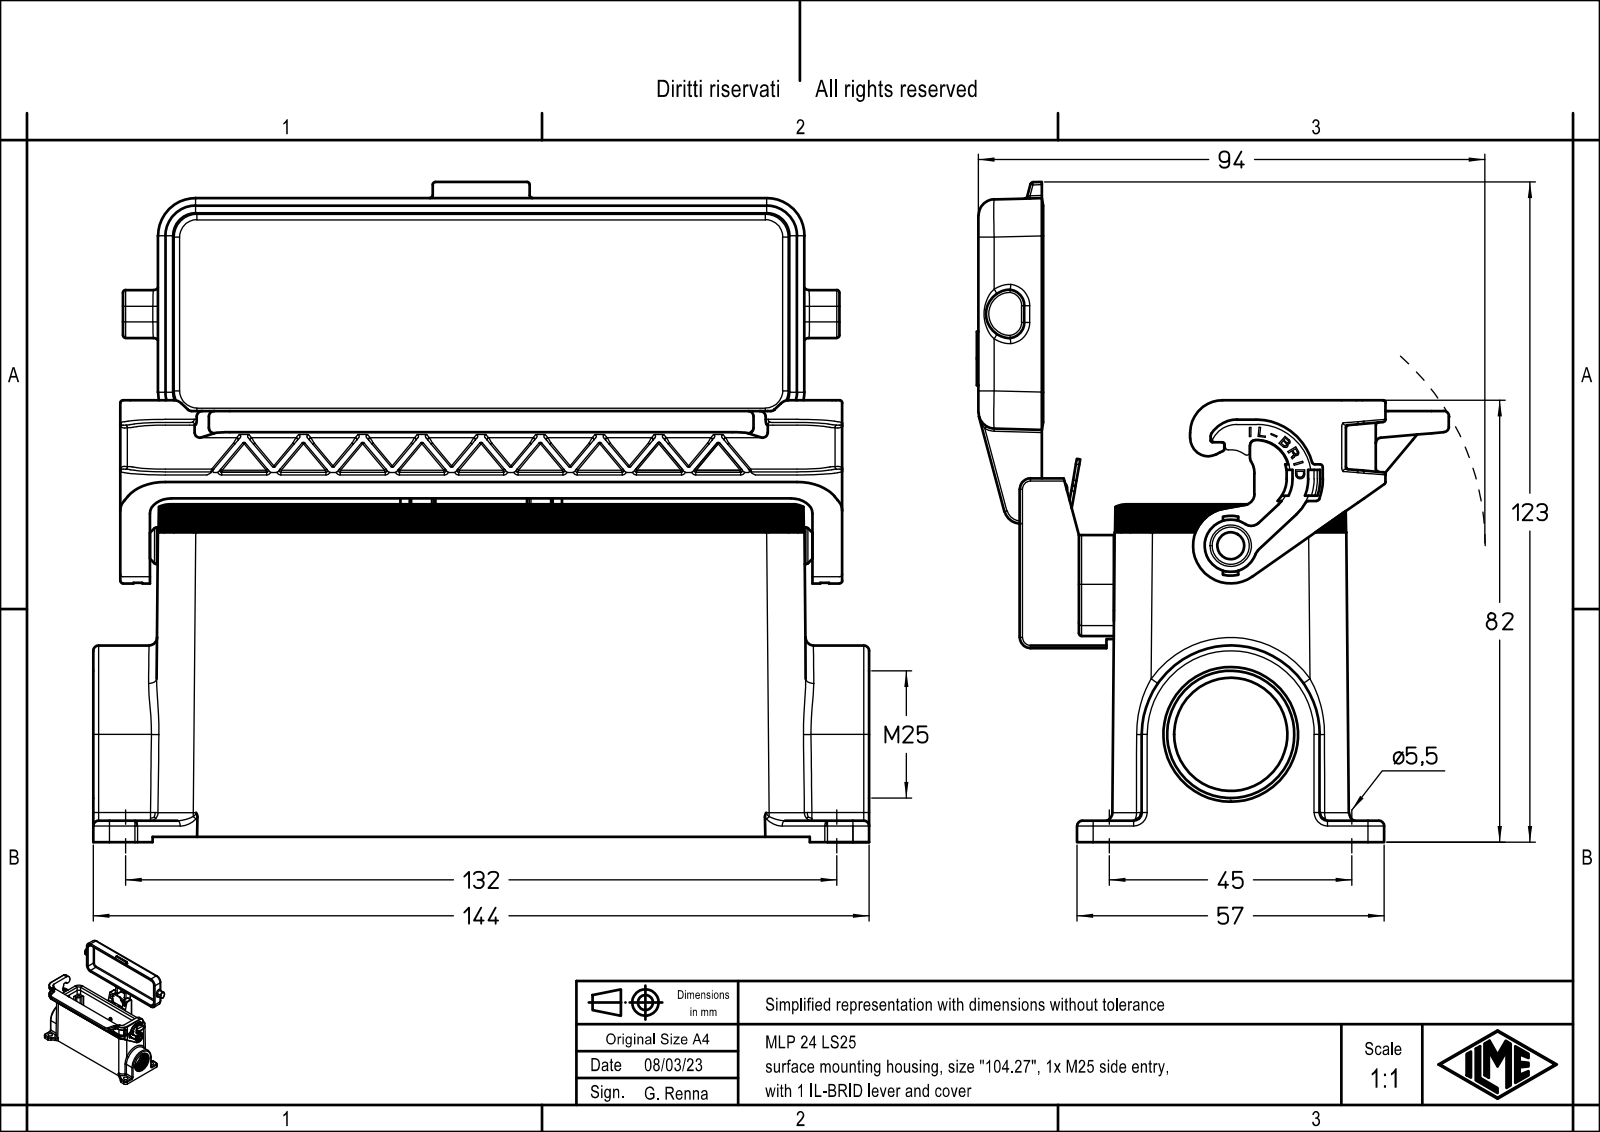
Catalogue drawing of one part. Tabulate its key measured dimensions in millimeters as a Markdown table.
| quantity | value |
| --- | --- |
| part name | MLP 24 LS25 |
| STEP written by | Creo Elements/Direct Modeling 20.1B 02-Apr-2019 (C) Parametric Technology GmbH (AUTOMOTIVE_DESIGN) |
| units | millimeters |
| bodies | 1 solid, 1423 faces (831 planar, 409 cylindrical, 183 other) |
| overall size | 144 × 122.49 × 87.8 |
| volume | 162 628 mm³ |
| surface area | 93 955 mm² |
| round holes (diameter × count) | 3 × 4, 3.5 × 4, 5.5 × 4, 3.25 × 1, 4.2 × 1, 5.4 × 1, 7.7 × 1, 21 × 1, 23.6 × 1 |
| round bosses / shafts (diameter × count) | 8.4 × 1, 6.9 × 1, 6.8 × 1, 5.2 × 1, 4 × 1, 3.2 × 1 |
| partial cylindrical surfaces (radius × count) | 0.5 × 29, 1 × 28, 0.1 × 27, 0.2 × 23, 3 × 23, 0.17 × 17, 0.33 × 16, 1.5 × 15 |
| main face-to-face distances | 2, 3, 2.8, 69.75, 71.75, 79, 76, 10.5, 133.5, 1 |
| hole center spacings | 16.64, 38.63, 118.34, 123.37, 27, 45, 104, 107.45 |
